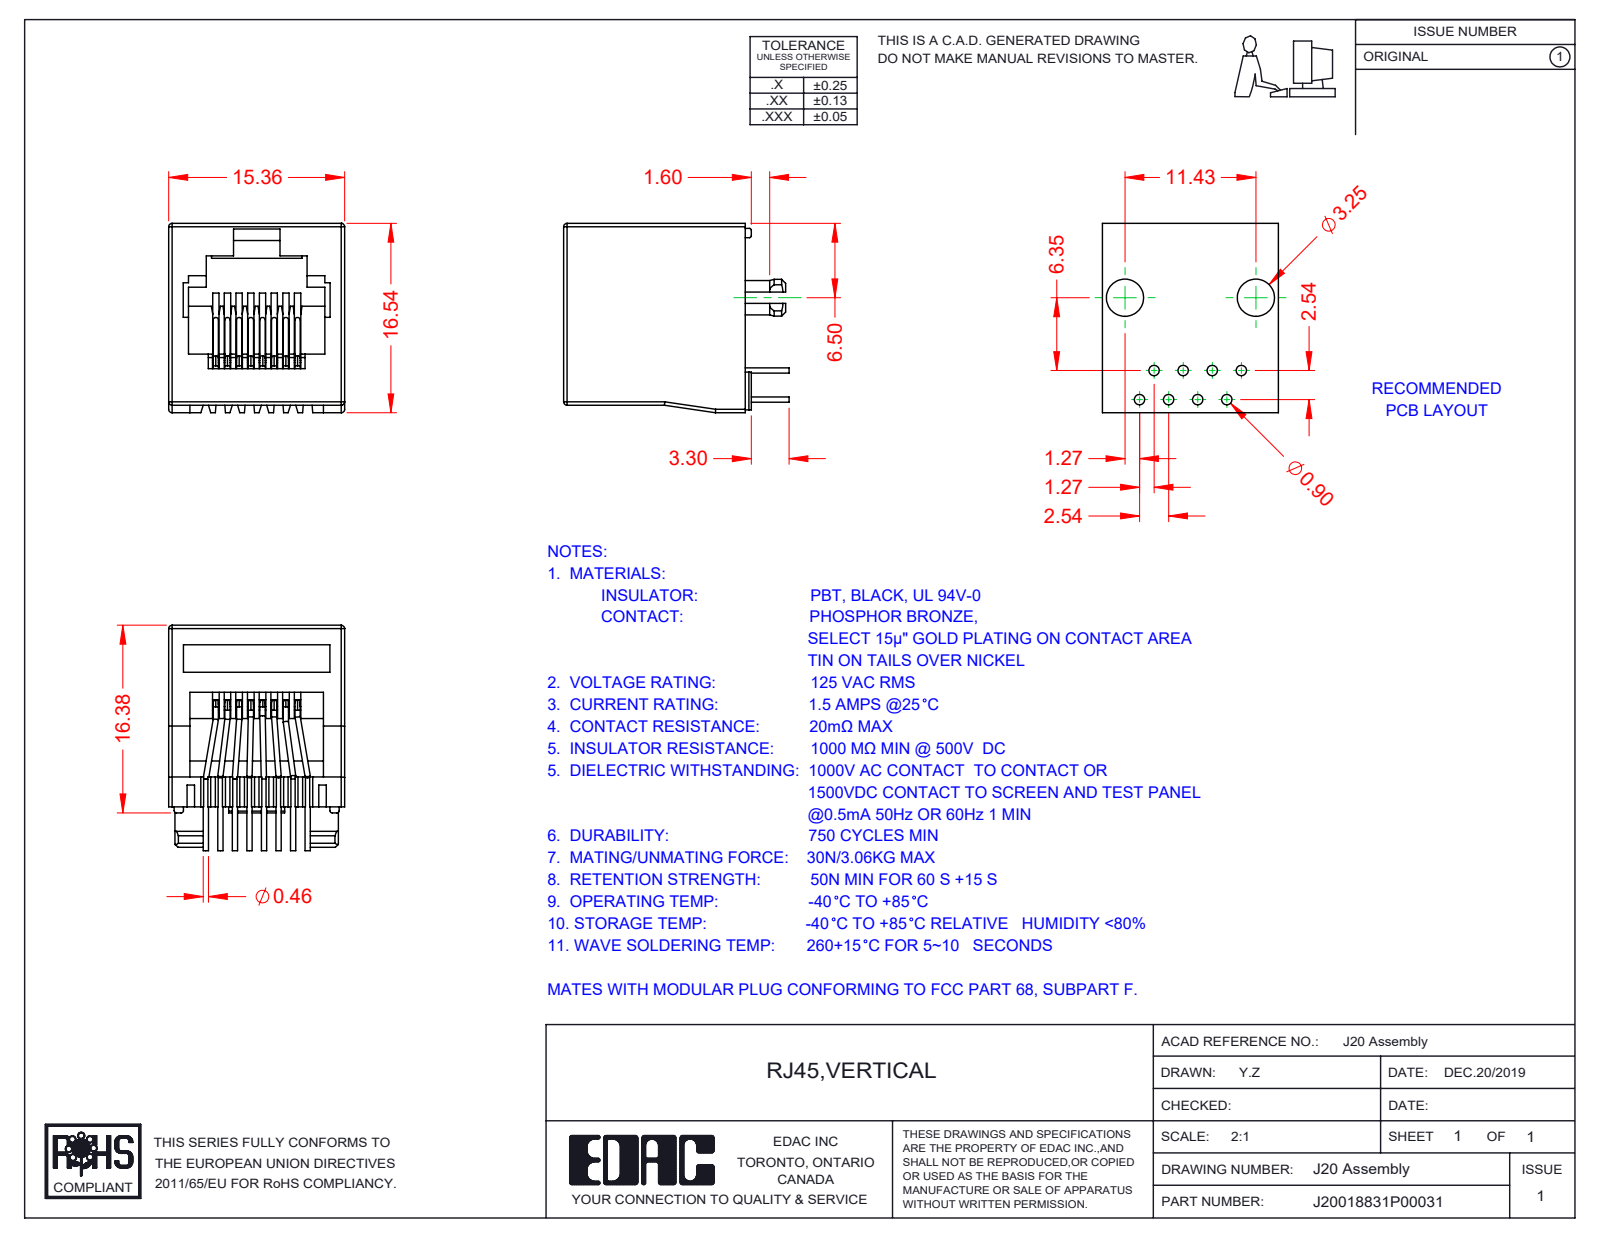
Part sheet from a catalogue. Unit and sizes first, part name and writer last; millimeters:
Units: millimetres
Overall size (bounding box): 19.68 × 16.54 × 15.36
Round holes (diameter × count): ⌀2 ×2
Round bosses / shafts (diameter × count): ⌀0.46 ×45
Partial cylindrical surfaces — rounded edges, fillets, slot ends (radius × count): R0.13 ×16, R0.3 ×13, R0.25 ×9, R0.2 ×5, R0.15 ×2, R1.5 ×2, R1.6 ×2
Main face-to-face distances: 15.36, 1.73, 2, 13.63, 0.45, 15.85, 1.28, 10.35, 1.5, 14.08
Hole centre spacings: 11.43
Volume: 1 935 mm³ · Surface area: 3 110 mm²
Bodies: 9 solids, 573 faces (332 planar, 193 cylindrical, 48 other)
Part name (STEP PRODUCT): RJ20018831P00031; 20 Contacts; 20 Insulator
STEP written by: SolidWorks 2016 (CONFIG_CONTROL_DESIGN)
